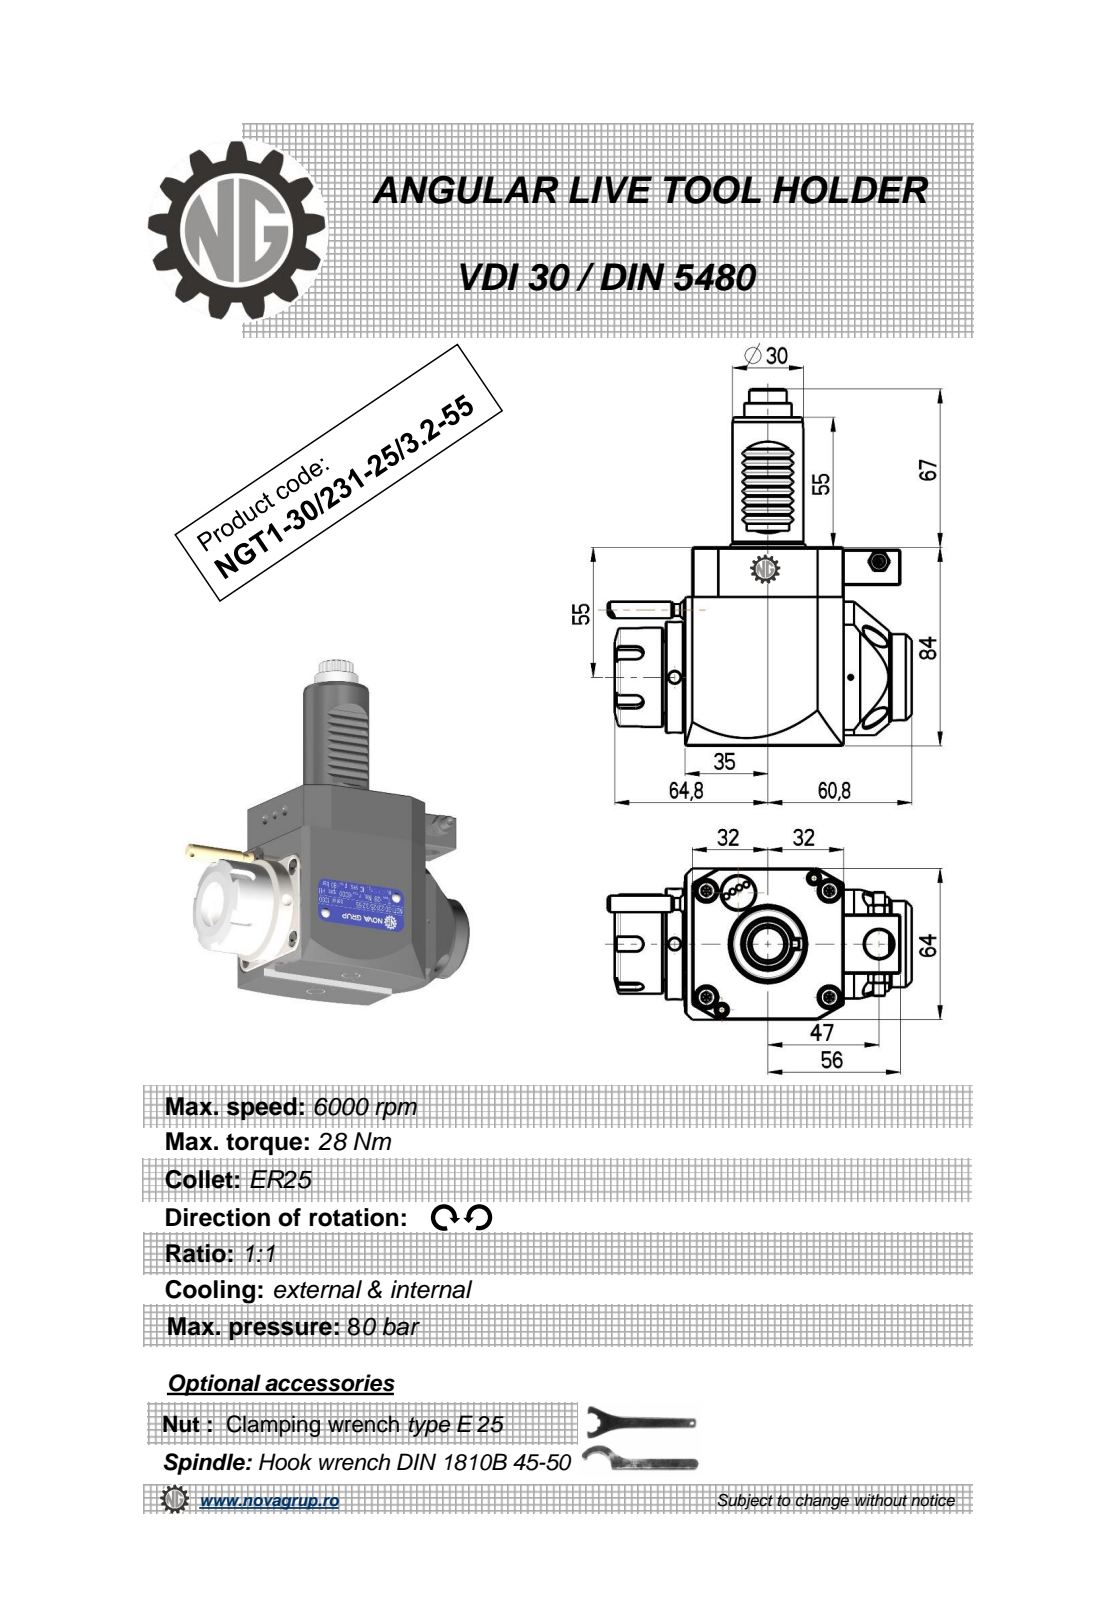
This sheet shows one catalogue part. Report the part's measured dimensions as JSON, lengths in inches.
{"part_name": "NGT1_30_231_25_3_2_55", "step_written_by": "PRO/ENGINEER BY PARAMETRIC TECHNOLOGY CORPORATION, 2010280 (CONFIG_CONTROL_DESIGN)", "units": "inches", "bodies": {"solids": 1, "faces": 507, "planar": 186, "cylindrical": 155, "other": 166}, "overall_size": [5.945, 5.064, 2.52], "volume_in3": 29.33, "surface_area_in2": 76.99, "round_holes": [[0.197, 2], [0.098, 1], [0.118, 1], [0.165, 1], [0.374, 1], [0.472, 1], [0.799, 1]], "round_bosses_or_shafts": [[0.353, 2], [0.197, 2], [1.85, 1], [1.654, 1], [1.437, 1], [1.378, 1], [1.181, 1], [0.787, 1]], "partial_cylinders_radius": [[0.078, 36], [0.01, 12], [0.012, 8], [0.118, 5], [6.299, 2], [0.279, 1], [0.312, 1], [0.512, 1]], "face_to_face_distances": [2.52, 3.307, 0.02, 2.646, 2.638, 0.295, 0.118, 0.126, 0.315, 2.165], "hole_center_spacings": [0.975, 1.307, 1.831, 3.404, 3.912]}
